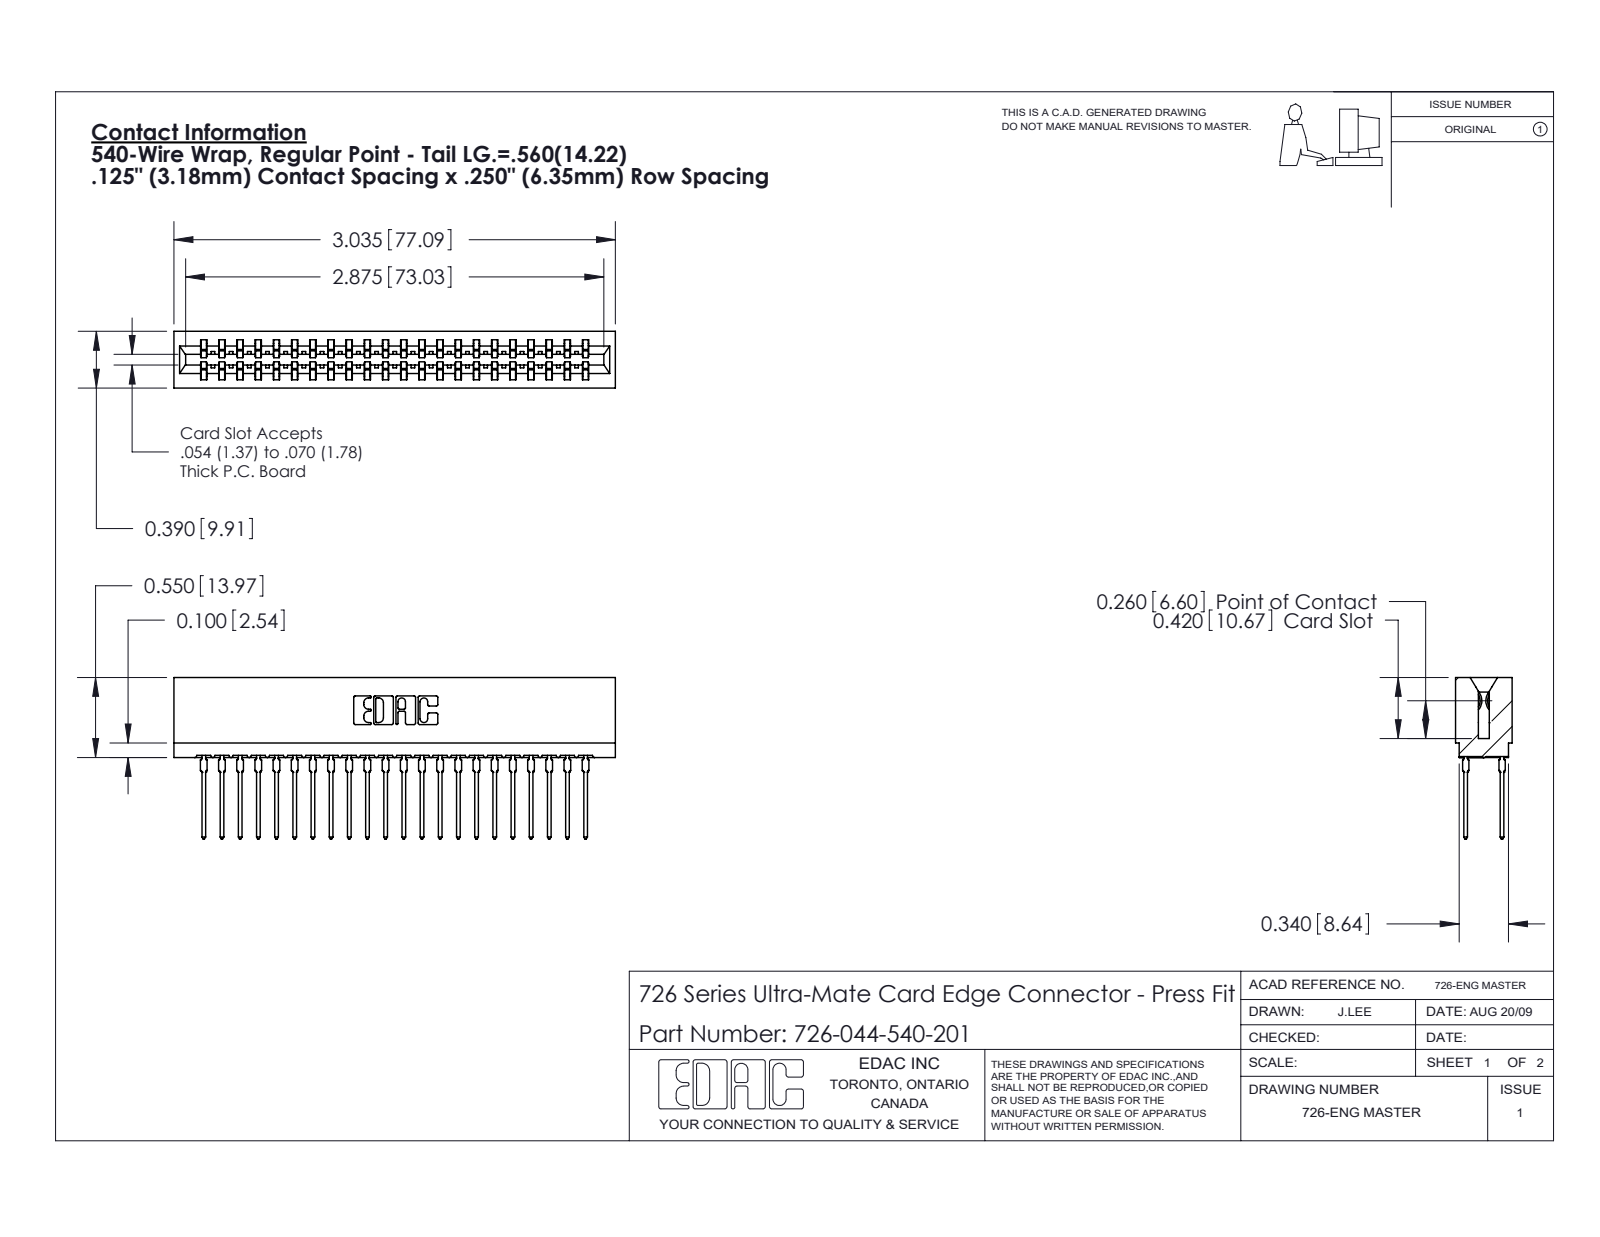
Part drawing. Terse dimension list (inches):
name: 746-292-001_540; 726-044-540-201; 726 Part_.515 Slot Depth - 01
written by: SolidWorks 2020 (CONFIG_CONTROL_DESIGN)
unit: in
bodies: 45 solids, 4035 faces (2079 planar, 812 cylindrical, 1144 other)
size: 3.035 × 1.109 × 0.39
volume: 0.448 in³; area: 19.35 in²
rounds: 88× R0.021, 23× R0.015, 22× R0.01, 8× R0.005, 8× R0.011, 6× R0.007, 6× R0.031, 3× R0.026
face distances: 0.057, 0.333, 0.025, 0.307, 0.25, 0.39, 0.083, 0.275, 0.042, 1.25
